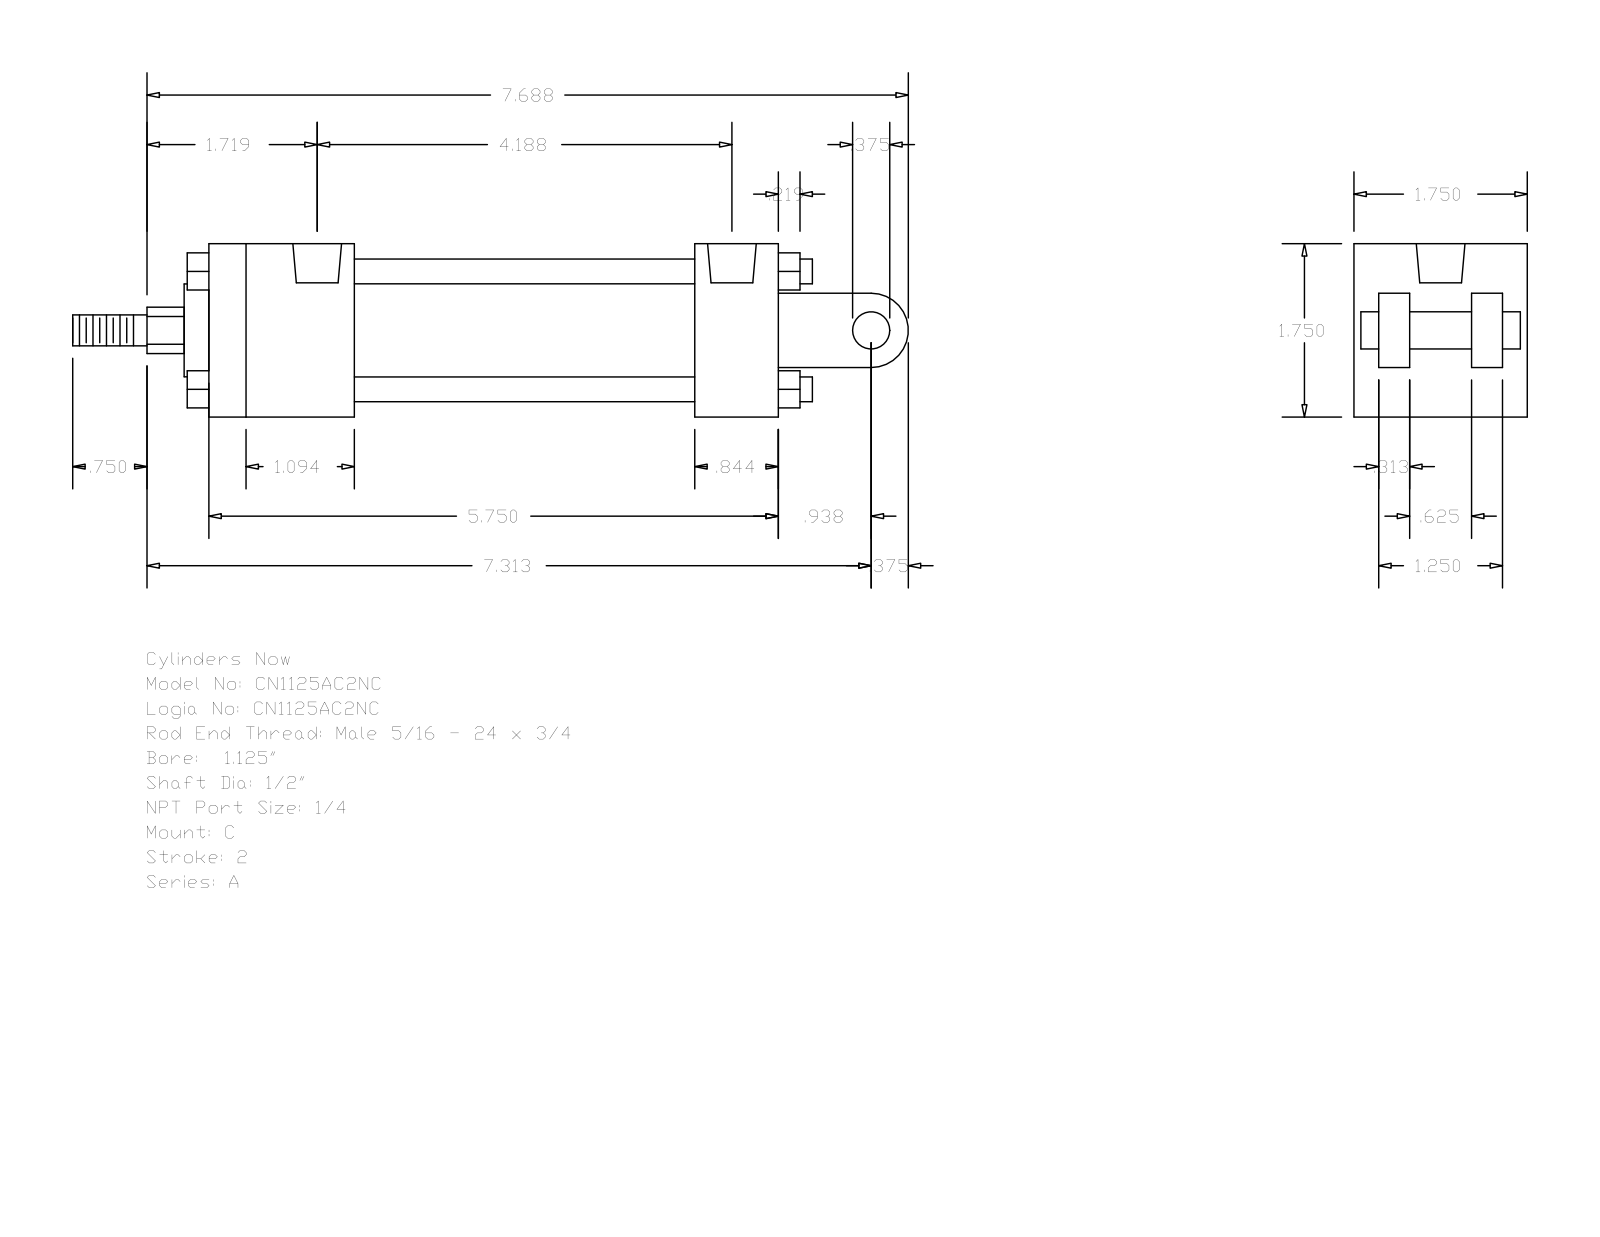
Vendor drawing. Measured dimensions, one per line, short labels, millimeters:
name: A_C__0112_0.5
written by: GSSL Pune (CONFIG_CONTROL_DESIGN)
unit: mm
bodies: 0 solids, 135 faces (102 planar, 33 cylindrical, 0 other)
size: 214.31 × 44.45 × 44.45
holes: 4× ⌀5.56, 2× ⌀12.49
bosses: 4× ⌀6.35, 1× ⌀31.88, 1× ⌀23.81, 1× ⌀12.7, 1× ⌀9.53, 1× ⌀7.94
rounds: 1× R5.94, 1× R9.53
face distances: 44.46, 6.35, 31.76, 14.29, 146.05, 30.17, 124.61, 21.44, 37.3, 87.31
hole spacings: 103.19, 1.58, 1.59, 104.77, 104.78, 106.36
